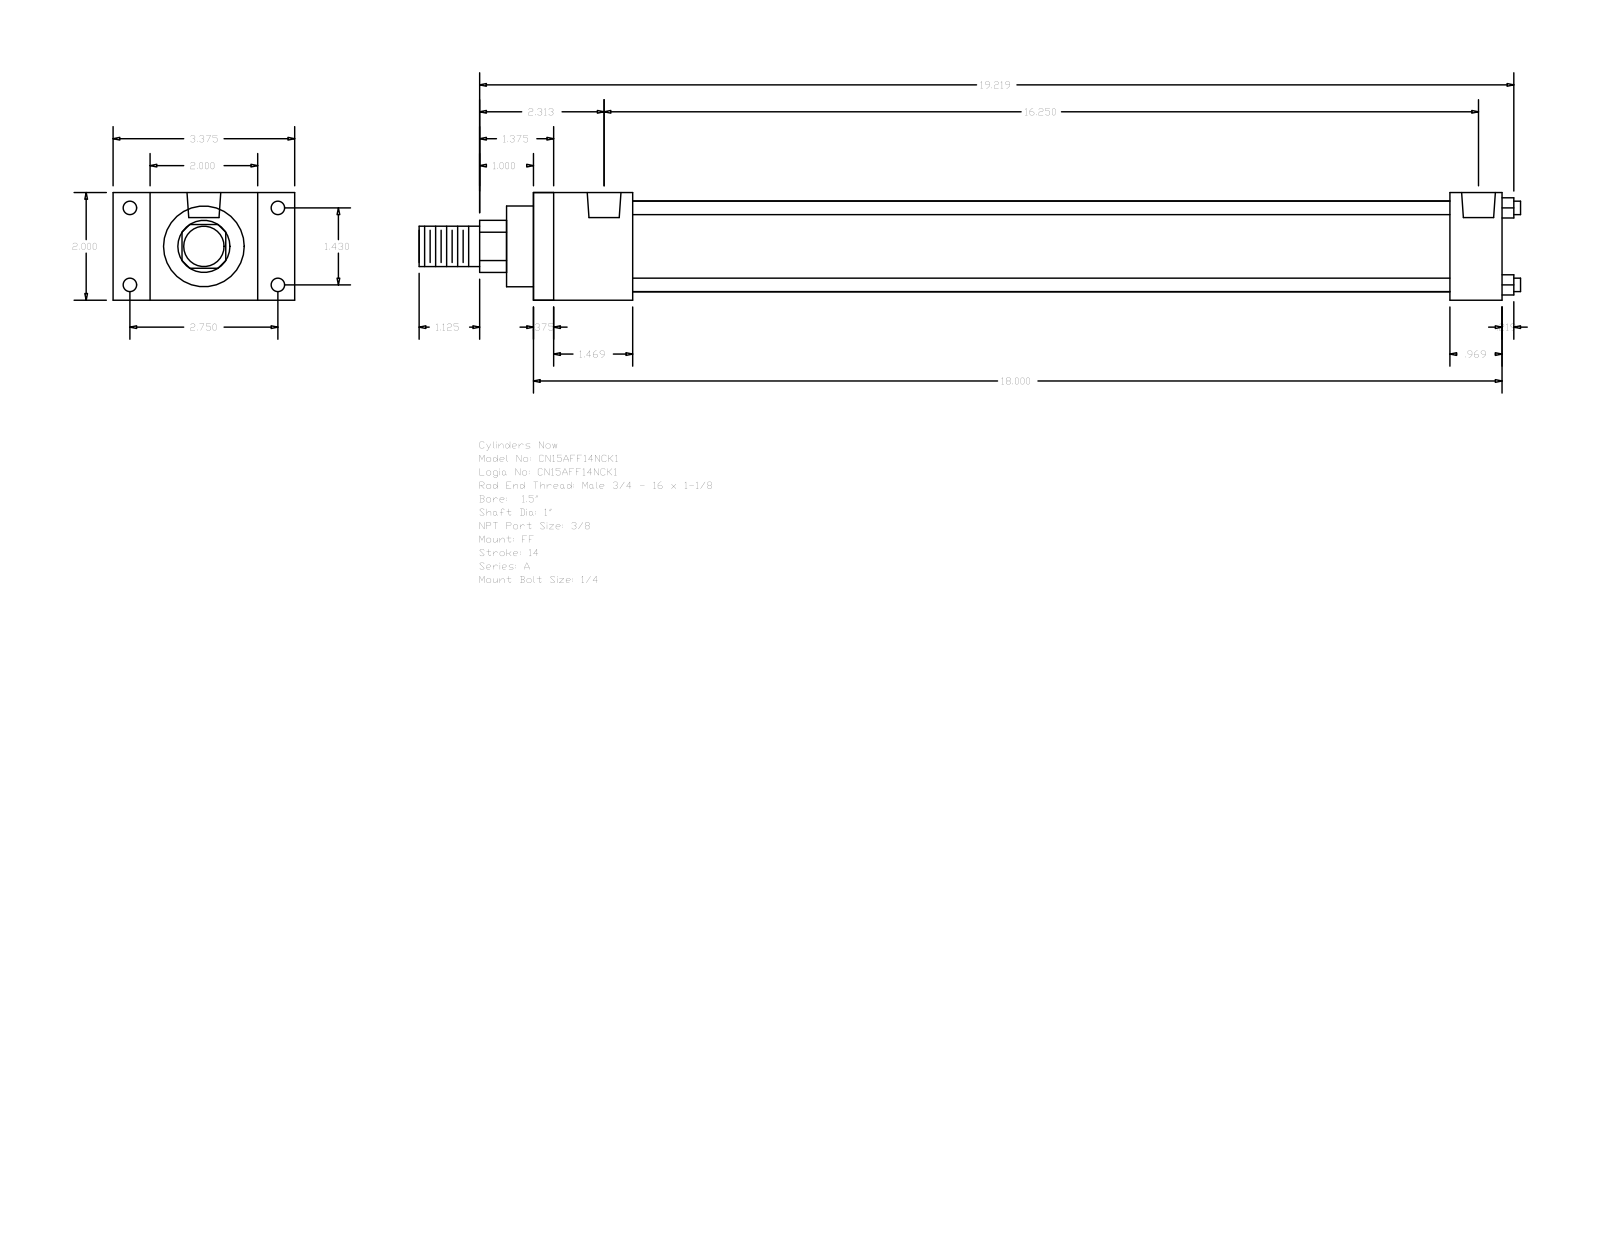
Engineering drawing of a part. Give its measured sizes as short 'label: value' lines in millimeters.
name: A_FF__0150_1
written by: GSSL Pune (CONFIG_CONTROL_DESIGN)
unit: mm
bodies: 0 solids, 92 faces (64 planar, 28 cylindrical, 0 other)
size: 519.91 × 85.72 × 50.8
holes: 4× ⌀5.56, 4× ⌀6.35, 2× ⌀15.93
bosses: 4× ⌀6.35, 1× ⌀42.93, 1× ⌀38.1, 1× ⌀25.4, 1× ⌀19.05
rounds: 1× R12.29
face distances: 50.8, 457.2, 9.52, 447.68, 46.83, 432.59, 37.31, 423.07, 385.76, 410.37
hole spacings: 3.97, 36.32, 69.84, 78.72, 404.81, 408.78, 412.75
